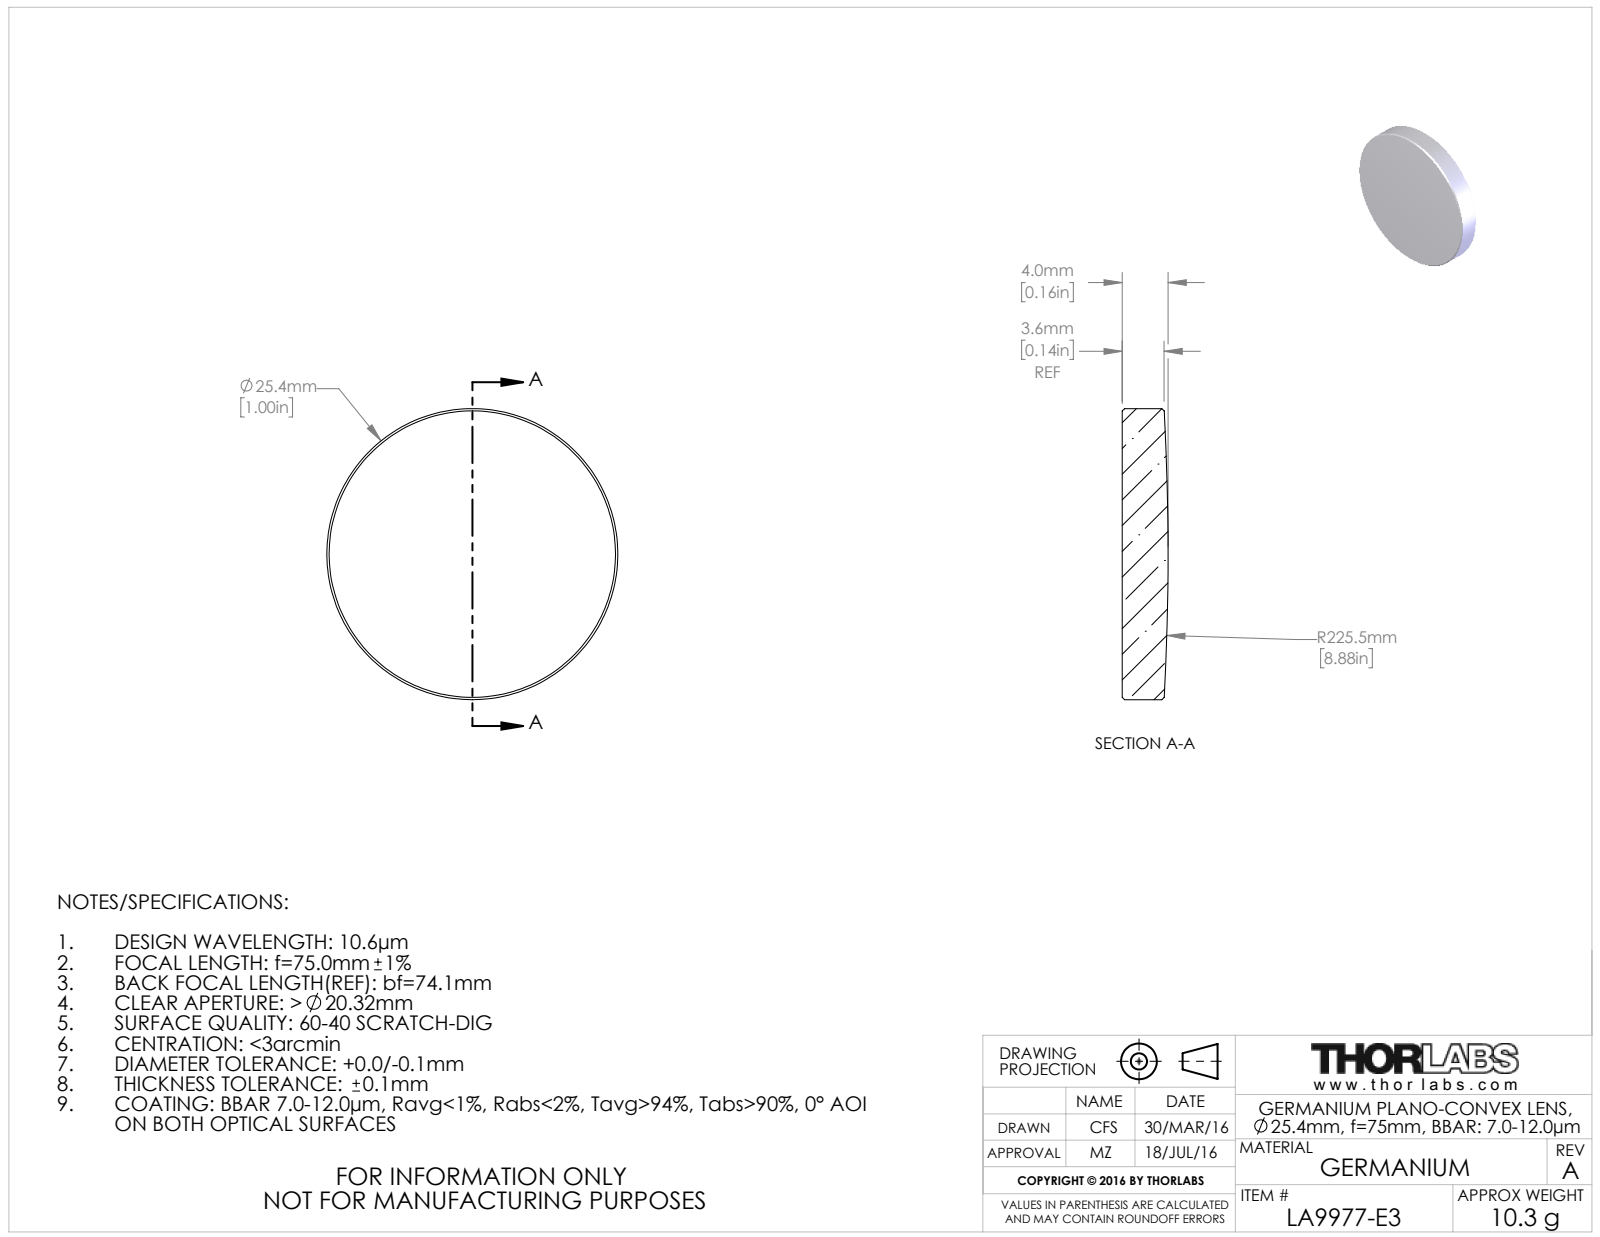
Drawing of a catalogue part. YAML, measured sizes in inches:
part_name: "TTN049393-E0W"
step_written_by: "SolidWorks 2016 (CONFIG_CONTROL_DESIGN)"
units: inches
bodies: {solids: 1, faces: 9, planar: 1, cylindrical: 2, other: 6}
overall_size: [1, 1, 0.157]
volume: 0.118
surface_area: 1.994
round_bosses_or_shafts:
  - {diameter: 1, count: 1}
